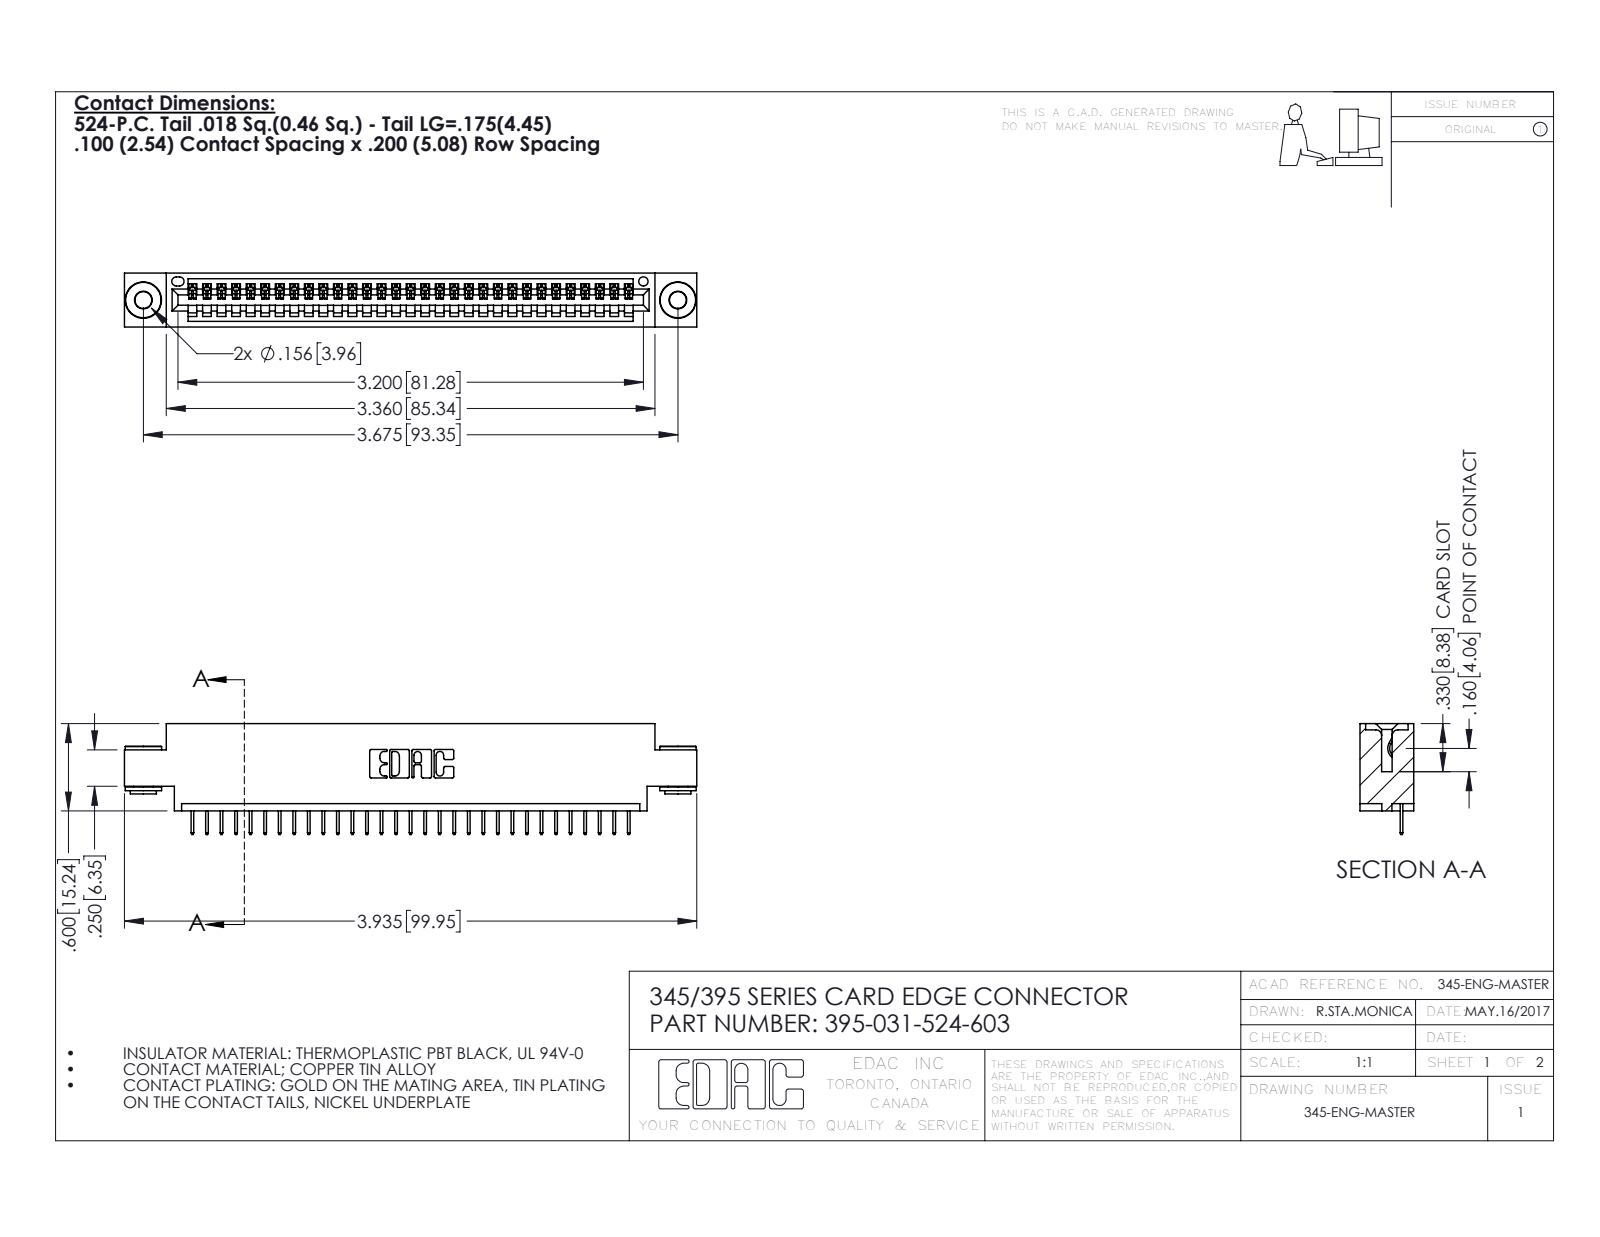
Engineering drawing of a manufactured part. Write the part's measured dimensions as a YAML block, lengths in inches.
part_name: "345-250-002_345-250-002-102; 395-031-524-603; 345-292-001_345-293-124; 345 Part_0.170 Offset - 0.156 Dia-TH"
step_written_by: "SolidWorks 2016 (CONFIG_CONTROL_DESIGN)"
units: inches
bodies: {solids: 34, faces: 2090, planar: 1520, cylindrical: 562, other: 8}
overall_size: [3.935, 0.762, 0.37]
volume: 0.561
surface_area: 18.61
round_holes:
  - {diameter: 0.116, count: 2}
  - {diameter: 0.156, count: 2}
  - {diameter: 0.064, count: 1}
round_bosses_or_shafts:
  - {diameter: 0.25, count: 2}
  - {diameter: 0.18, count: 2}
  - {diameter: 0.136, count: 2}
partial_cylinders:
  - {radius: 0.006, count: 62}
  - {radius: 0.01, count: 22}
  - {radius: 0.007, count: 6}
  - {radius: 0.031, count: 6}
  - {radius: 0.026, count: 3}
  - {radius: 0.031, count: 2}
  - {radius: 0.04, count: 2}
  - {radius: 0.014, count: 1}
face_to_face_distances: [0.072, 0.298, 0.37, 0.2, 0.098, 0.272, 0.025, 0.225, 0.175, 0.072]
hole_center_spacings: [0.27, 3.44, 3.675]
